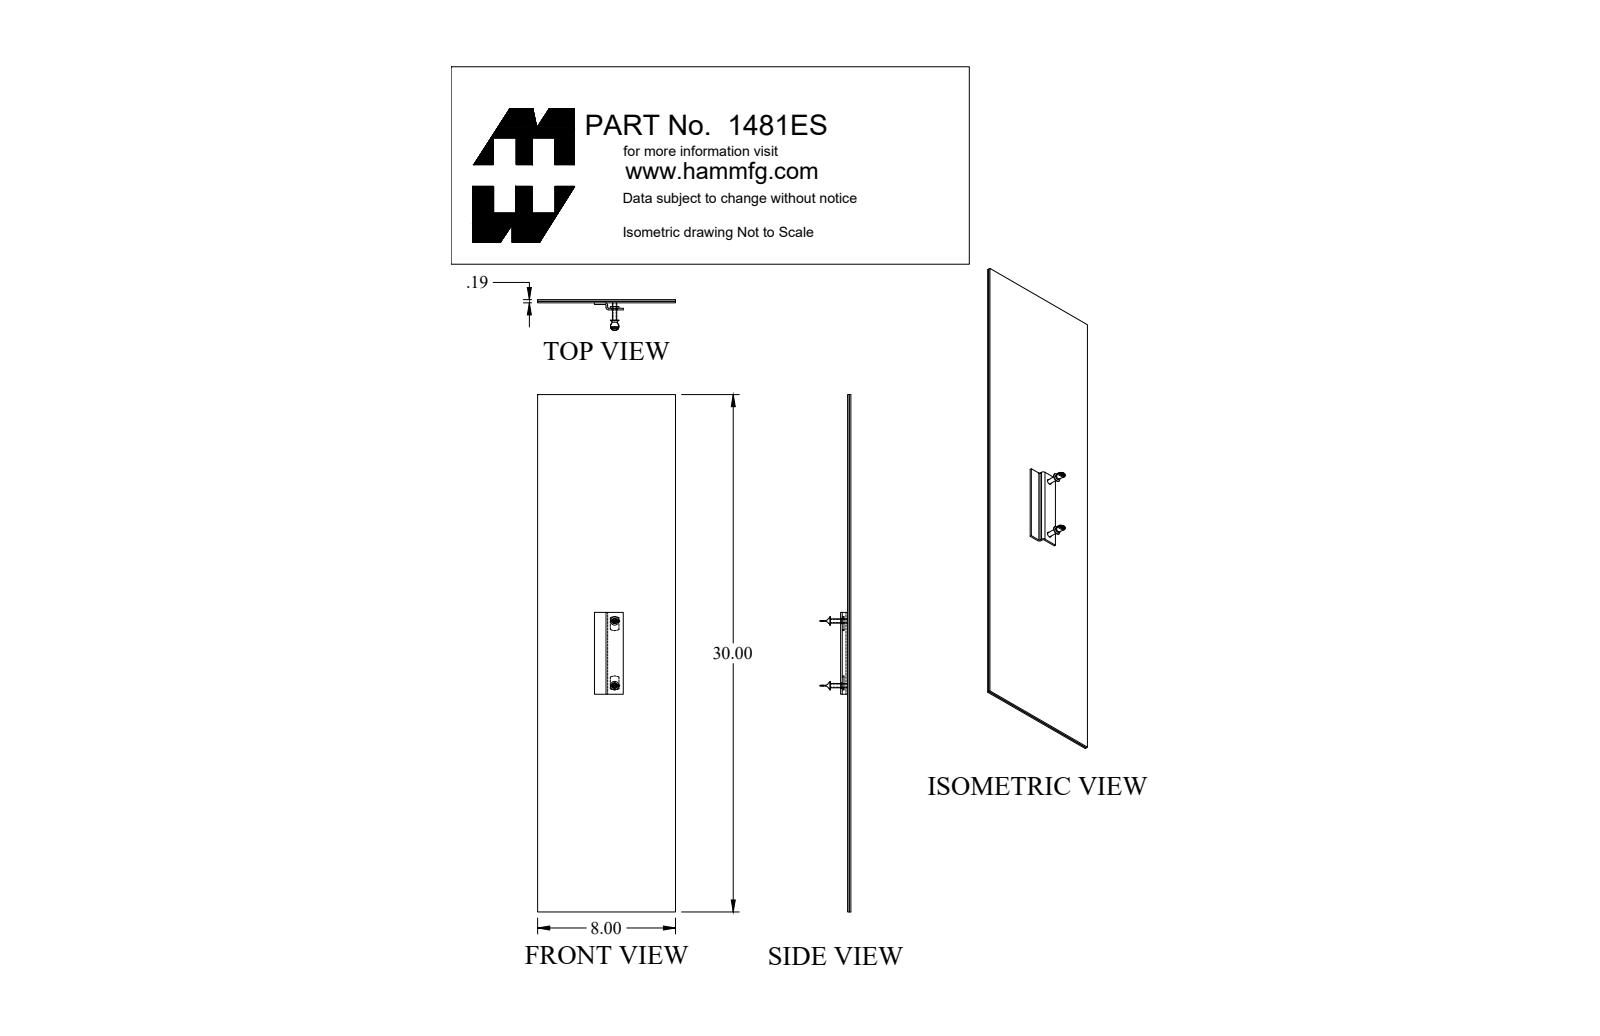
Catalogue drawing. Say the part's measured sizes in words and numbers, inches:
The part is named "1481ES_Default". Its 3-D file was written by "SolidWorks 2019 (CONFIG_CONTROL_DESIGN)". It is 7 solids with 126 faces: 54 planar, 48 cylindrical and 24 other. Overall it measures 30 by 8 by 1.79 inches. Its volume is 46.66 cubic inches and its surface area 999.1 square inches. Round holes: 2 of diameter 0.201, 2 of diameter 0.312. Round bosses or shafts: 2 of diameter 0.485, 2 of diameter 0.293, 2 of diameter 0.25. Partial cylindrical surfaces (rounded edges, fillets, slot ends): 12 of radius 0.005, 4 of radius 0.01, 4 of radius 0.2, 4 of radius 0.5, 2 of radius 0.048, 2 of radius 0.143. The main face-to-face distances are 0.095, 0.19, 0.502, 0.407, 8, 0.312, 0.597, 0.285, 0.19, 0.095. The hole center spacings are 3.75, 3.75, 3.75.
